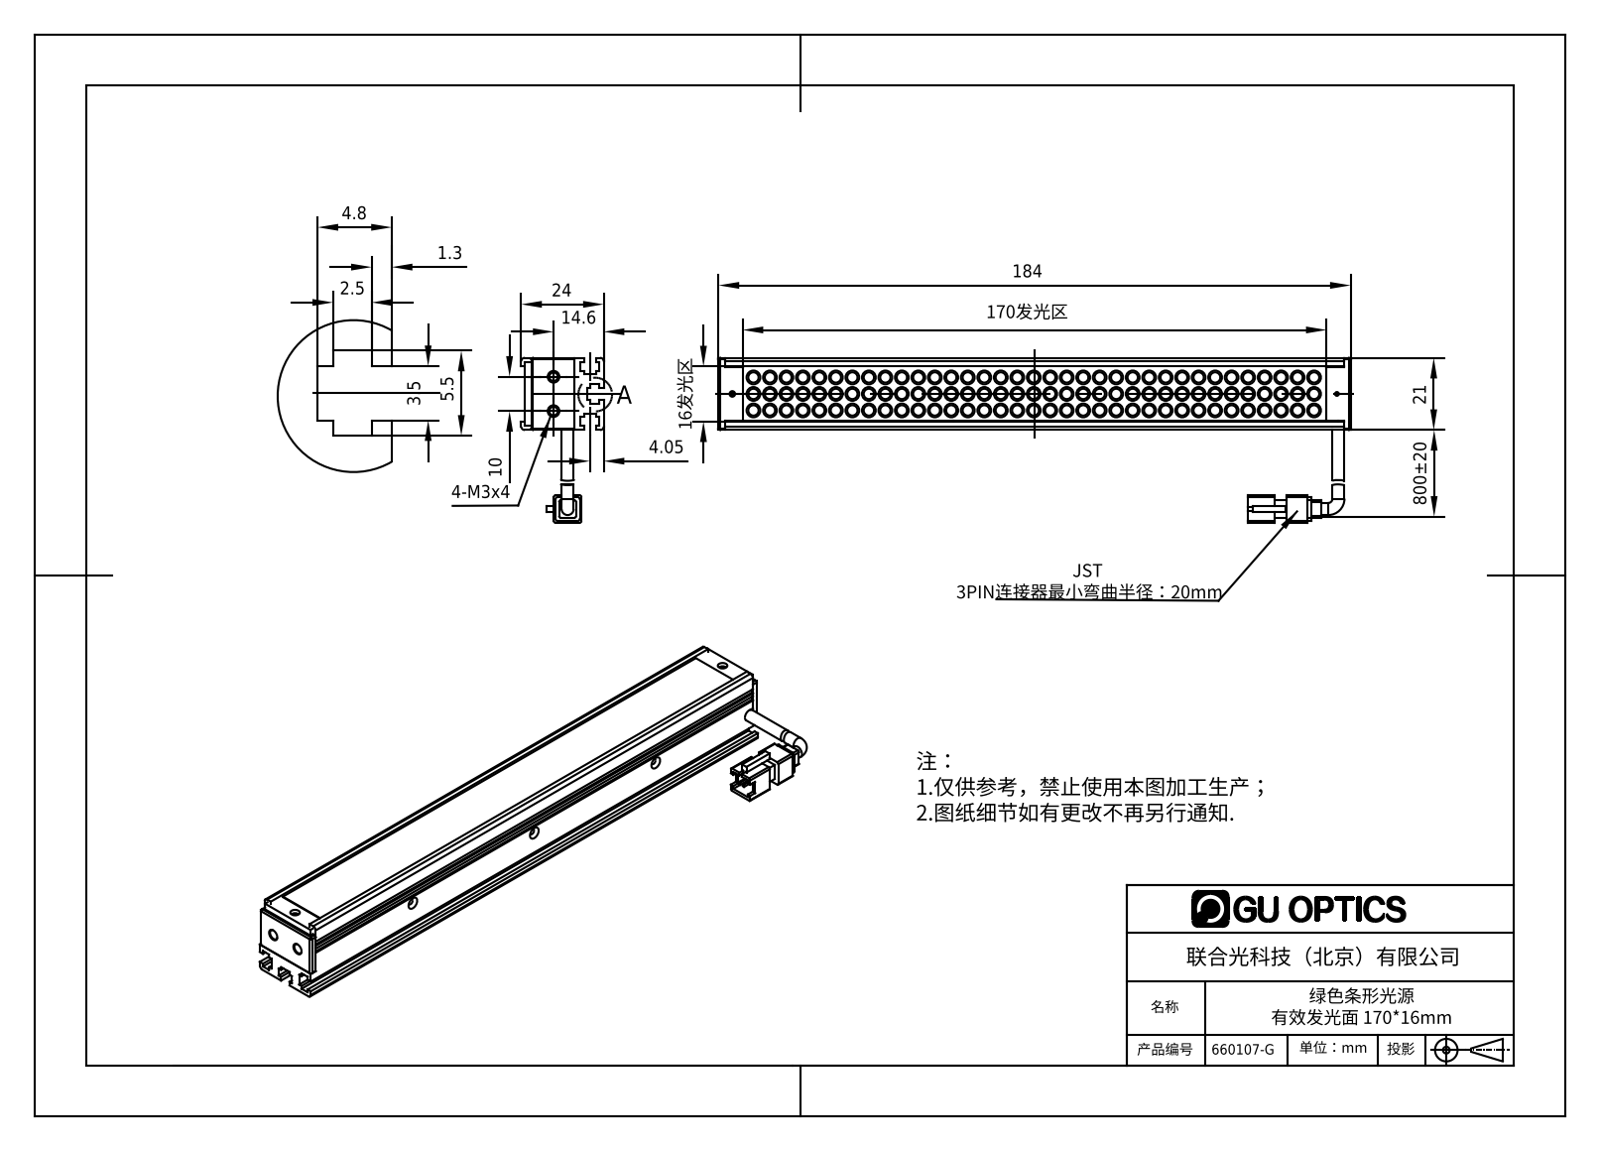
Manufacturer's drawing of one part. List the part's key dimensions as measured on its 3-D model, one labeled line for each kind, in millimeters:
Part name (STEP PRODUCT): 660107-G
STEP written by: SolidWorks 2016 (AUTOMOTIVE_DESIGN)
Units: millimetres
Bodies: 8 solids, 1075 faces (356 planar, 507 cylindrical, 212 other)
Overall size (bounding box): 184 × 48 × 24
Volume: 53 223 mm³ · Surface area: 59 208 mm²
Round holes (diameter × count): ⌀1.6 ×5, ⌀1.7 ×3, ⌀1.5 ×2, ⌀2.5 ×2, ⌀2.8 ×2, ⌀3 ×2, ⌀1.1 ×1, ⌀1.25 ×1, ⌀2 ×1
Round bosses / shafts (diameter × count): ⌀4 ×105, ⌀3 ×105, ⌀3.5 ×2
Partial cylindrical surfaces — rounded edges, fillets, slot ends (radius × count): R1 ×12, R0.5 ×8, R1.65 ×1
Main face-to-face distances: 1, 2.5, 2, 18.5, 21, 4, 14.6, 1.3, 2.2, 3.5
Hole centre spacings: 176, 7, 38.03, 38.38, 50, 88.01, 88.17, 138.01
